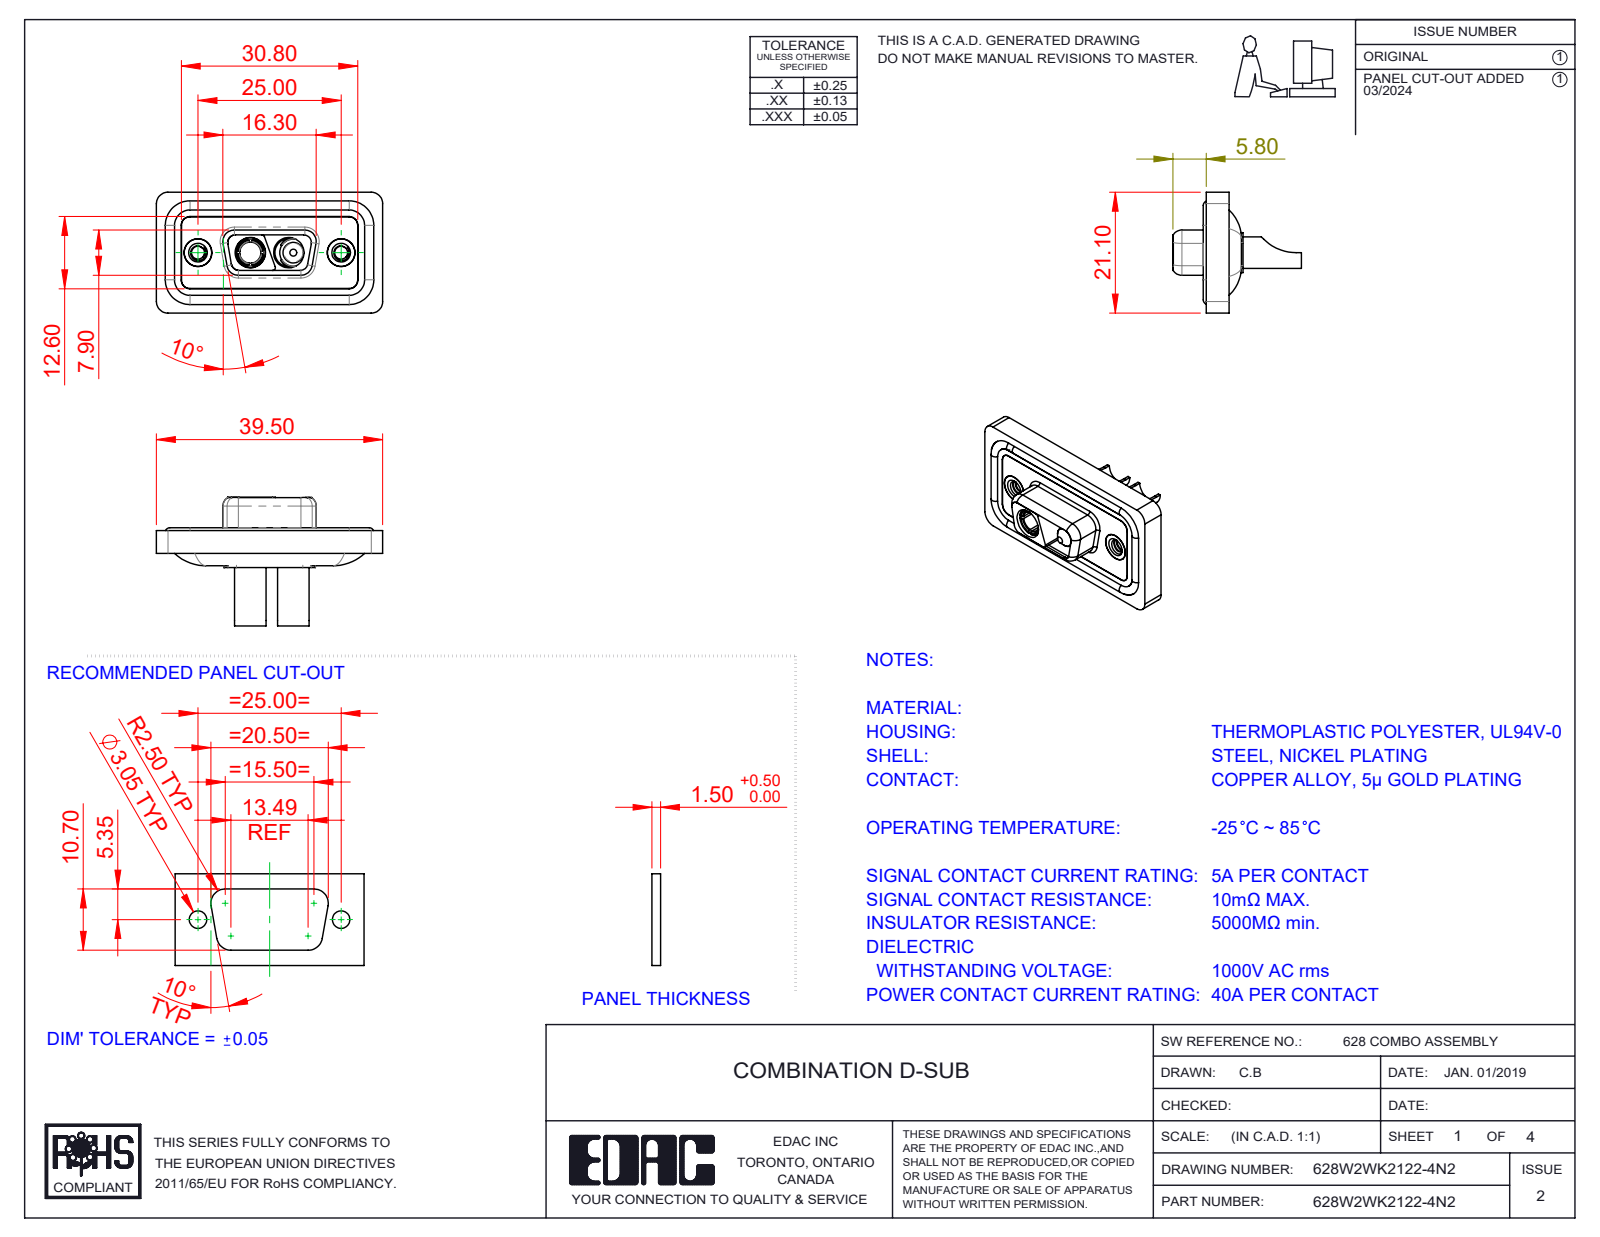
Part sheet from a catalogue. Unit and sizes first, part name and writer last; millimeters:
Units: millimetres
Overall size (bounding box): 39.5 × 22.45 × 21.1
Round holes (diameter × count): ⌀4.85 ×4, ⌀2.26 ×2, ⌀4 ×2, ⌀4.05 ×2, ⌀4.6 ×2, ⌀5 ×2, ⌀5.3 ×2, ⌀3.7 ×1
Round bosses / shafts (diameter × count): ⌀1.6 ×4, ⌀5.5 ×2, ⌀5.2 ×2, ⌀4.95 ×2, ⌀4.8 ×2, ⌀4.75 ×2, ⌀3.75 ×2, ⌀4.96 ×1
Partial cylindrical surfaces — rounded edges, fillets, slot ends (radius × count): R1.5 ×22, R2 ×18, R1.35 ×8, R1.6 ×8, R0.5 ×6, R0.25 ×4, R0.6 ×4, R0.65 ×4
Main face-to-face distances: 0.4, 1.1, 2.9, 1.6, 0.5, 1.8, 5.65, 5.35, 3.1, 0.7
Hole centre spacings: 9.14, 15.86, 6.72, 25
Volume: 4 683 mm³ · Surface area: 7 623 mm²
Bodies: 11 solids, 506 faces (148 planar, 233 cylindrical, 125 other)
Part name (STEP PRODUCT): 628W2WK2122-4N2; 628Combo Shell Rear_09 Contacts; Power Socket_40A SC; Power Pin_40A SC (+4 more)
STEP written by: SolidWorks 2023 (CONFIG_CONTROL_DESIGN)
